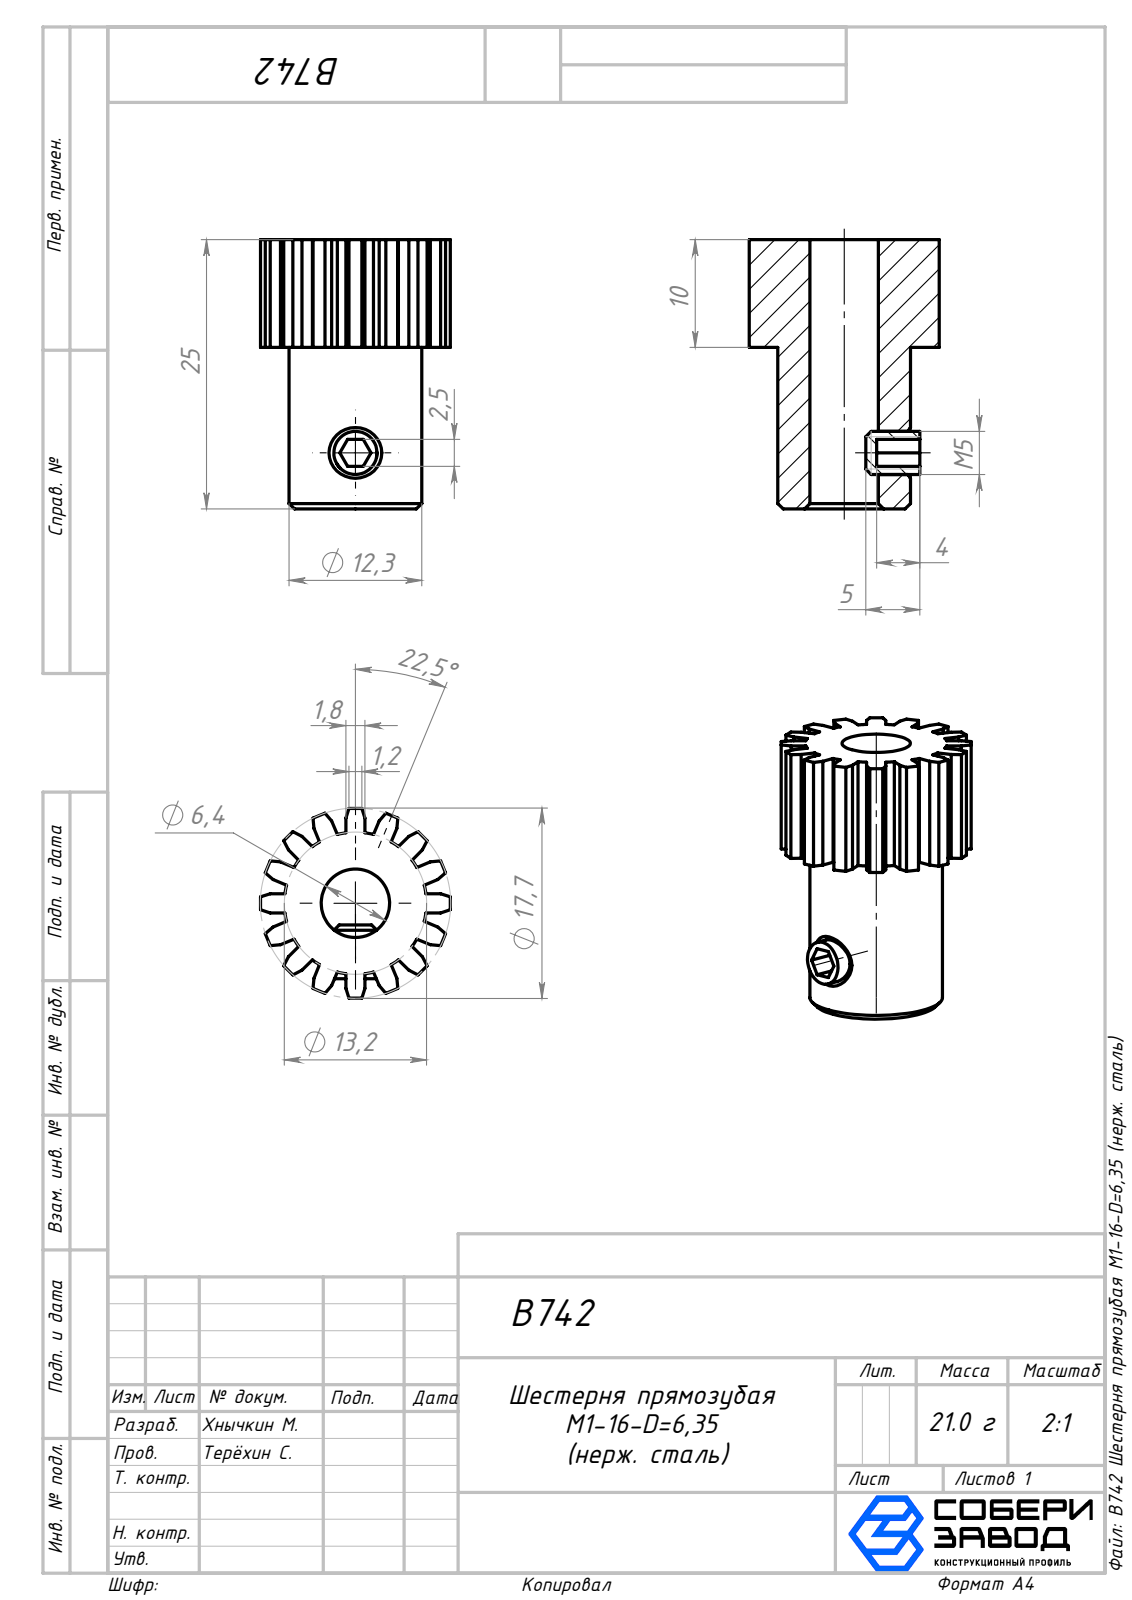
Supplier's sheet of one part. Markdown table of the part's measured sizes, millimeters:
| quantity | value |
| --- | --- |
| part name | Мелкая часть_00; B742 Шестерня прямозубая M1-16-D=6,35 (нерж. сталь)_00; B742 Шестерня прямозубая M1-16-D=6,35 (нерж. сталь) |
| STEP written by | SolidWorks 2025 (AUTOMOTIVE_DESIGN) |
| units | millimeters |
| bodies | 2 solids, 124 faces (92 planar, 24 cylindrical, 8 other) |
| overall size | 25 × 17.62 × 17.62 |
| volume | 2 945 mm³ |
| surface area | 2 581 mm² |
| round holes (diameter × count) | 4 × 1, 6.35 × 1 |
| round bosses / shafts (diameter × count) | 12.3 × 1 |
| partial cylindrical surfaces (radius × count) | 6.6 × 1 |
| main face-to-face distances | 1.78, 7.92, 9.7, 6.5, 17.62, 10, 15, 25, 6.48, 2.52 |
